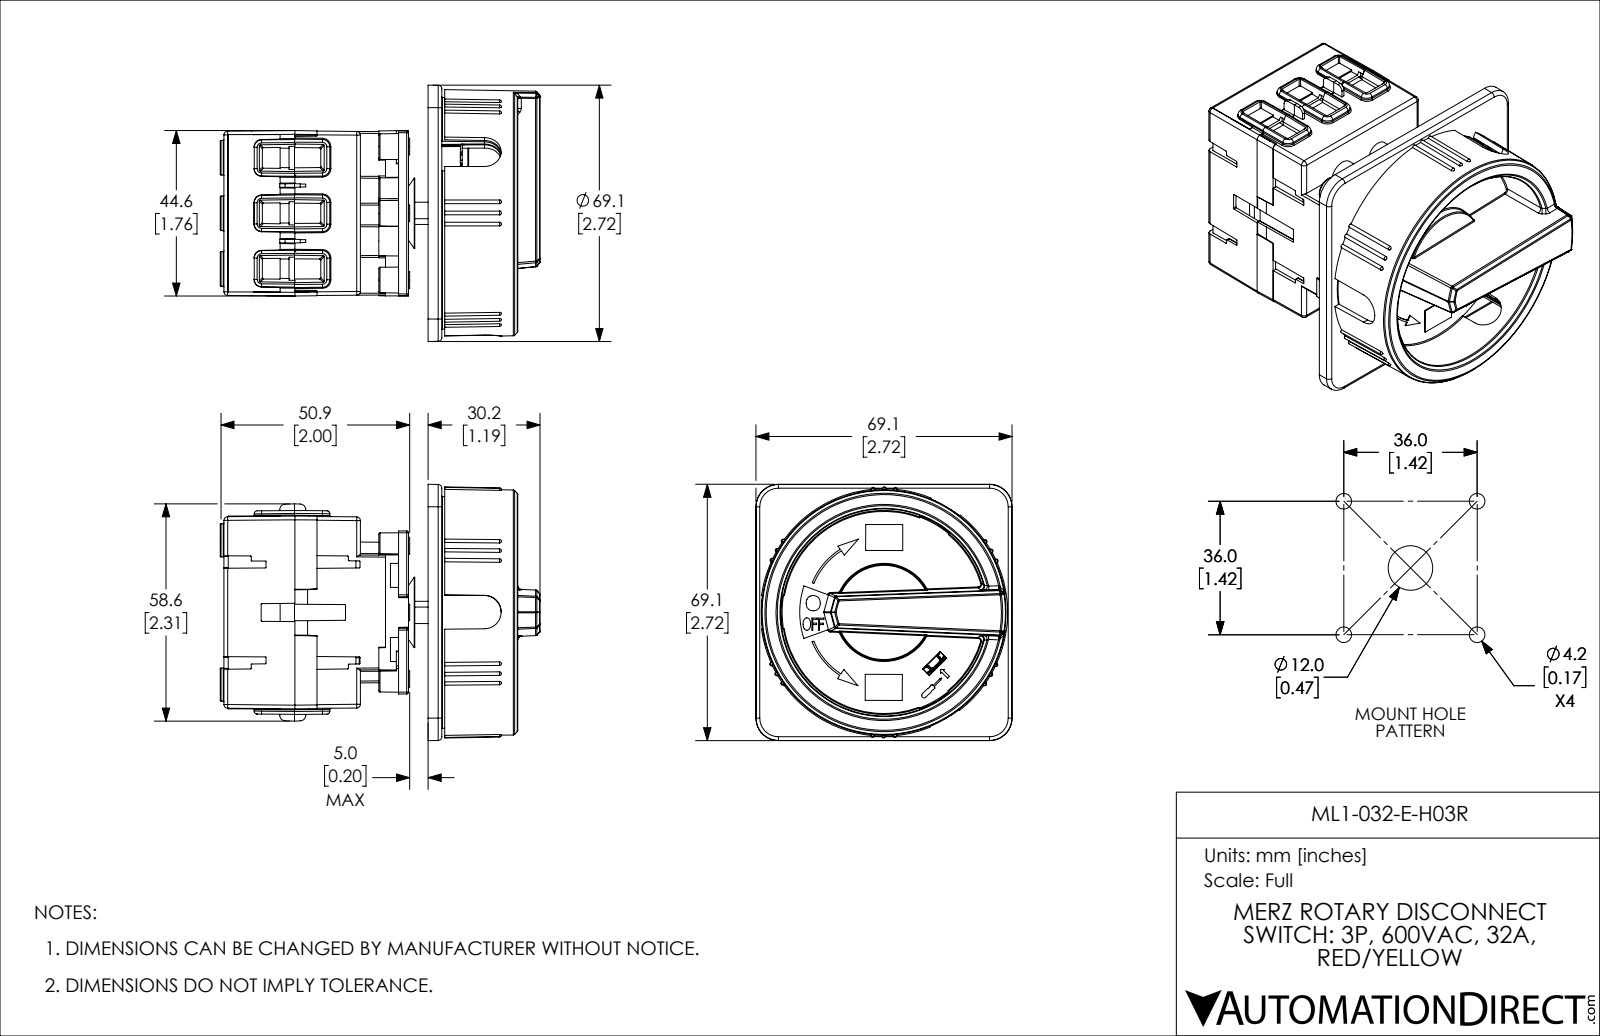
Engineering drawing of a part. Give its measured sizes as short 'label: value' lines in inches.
name: ML1-032-E-H03R
written by: SolidWorks 2019 (AUTOMOTIVE_DESIGN)
unit: in
bodies: 1 solid, 2964 faces (1185 planar, 610 cylindrical, 1169 other)
size: 3.398 × 2.722 × 2.722
volume: 8.361 in³; area: 101.4 in²
bosses: 2× ⌀0.071, 1× ⌀0.748, 1× ⌀0.236
rounds: 132× R0.02, 68× R0.012, 50× R0.039, 44× R0.008, 41× R0.008, 39× R0.01, 34× R0.031, 12× R0.079
face distances: 0.059, 0.138, 0.197, 0.079, 0.276, 0.571, 0.02, 0.551, 0.295, 0.807
